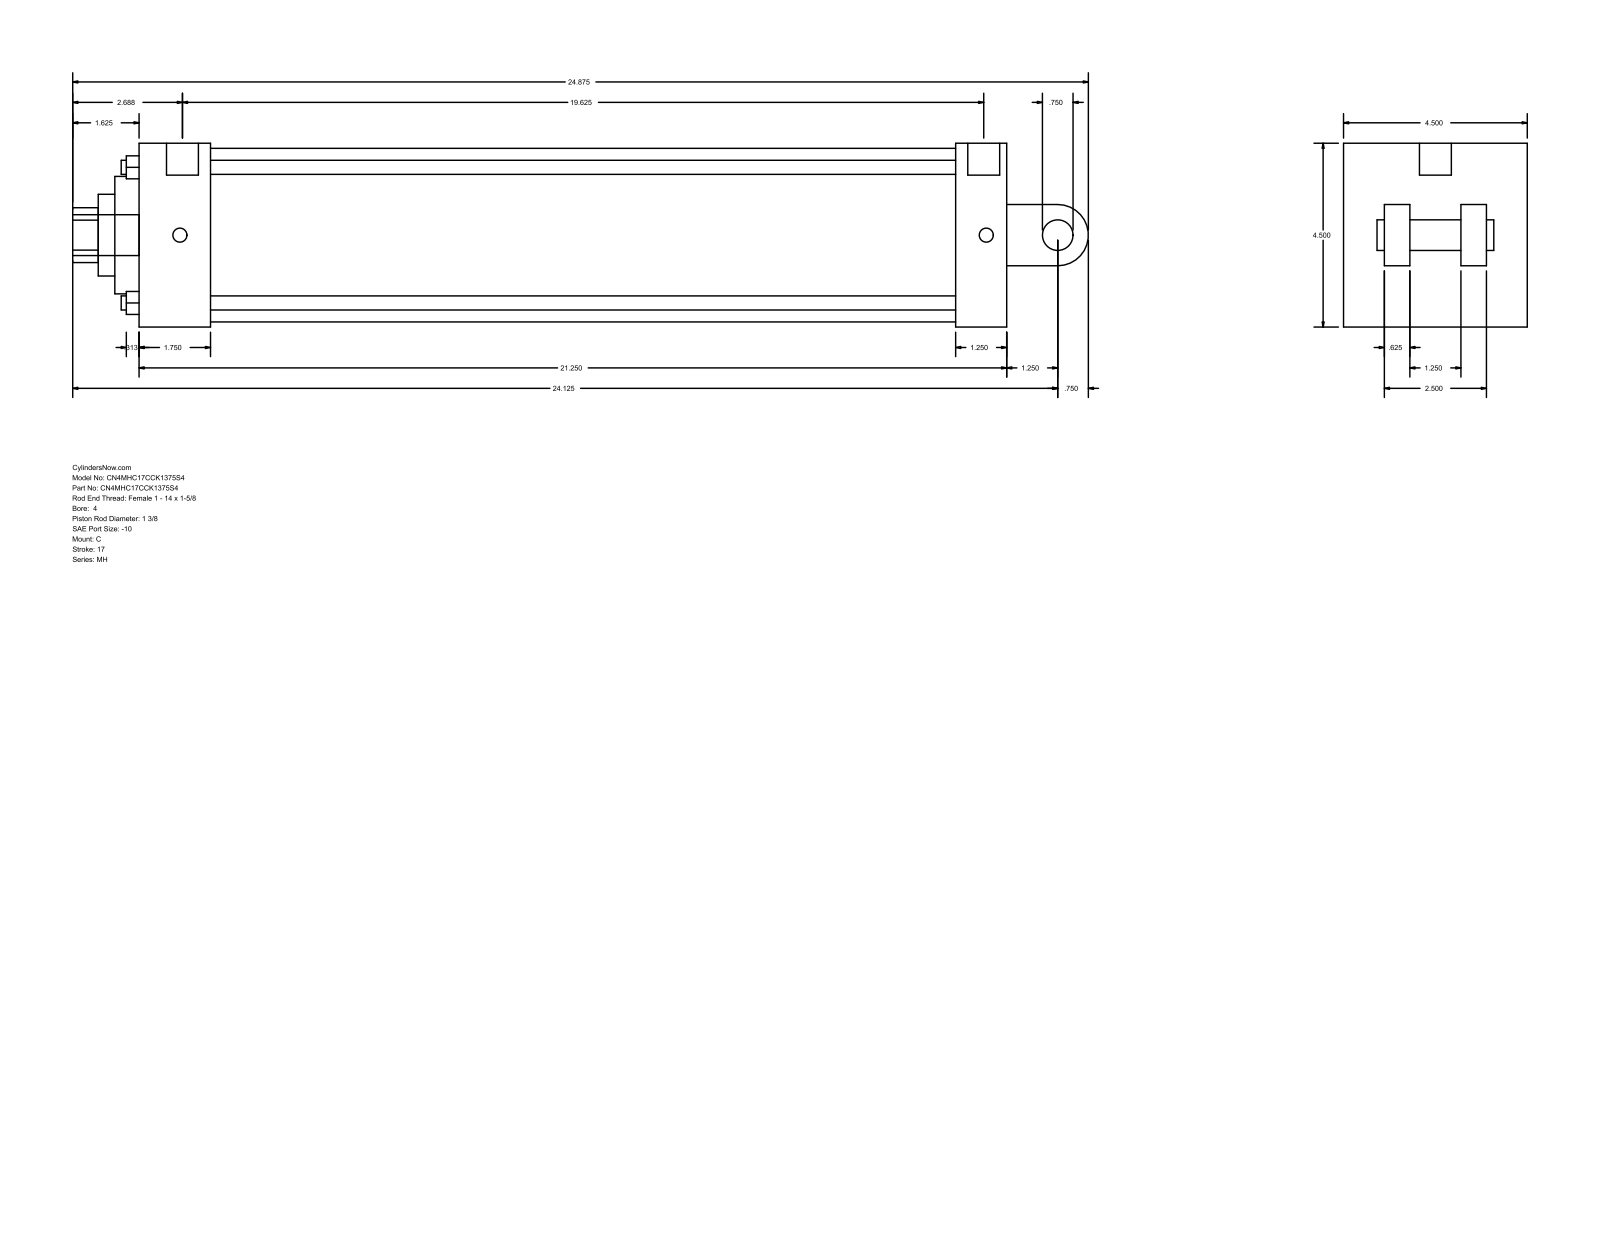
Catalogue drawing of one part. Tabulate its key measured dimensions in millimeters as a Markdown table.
| quantity | value |
| --- | --- |
| part name | MH_C__0400_1.375 |
| STEP written by | GSSL Pune (CONFIG_CONTROL_DESIGN) |
| units | millimeters |
| bodies | 0 solids, 101 faces (71 planar, 30 cylindrical, 0 other) |
| overall size | 631.83 × 114.3 × 114.3 |
| round holes (diameter × count) | 8.76 × 4, 8.73 × 2, 19.84 × 1, 34.92 × 1, 50.8 × 1, 73.03 × 1, 107.95 × 1 |
| round bosses / shafts (diameter × count) | 8.73 × 2, 25.4 × 1, 19.84 × 1, 19.05 × 1 |
| partial cylindrical surfaces (radius × count) | 17.06 × 1, 19.05 × 1 |
| main face-to-face distances | 114.3, 539.75, 44.45, 508, 463.55, 495.3, 31.75, 73.03, 41.27, 38.1 |
| hole center spacings | 59.62, 84.32, 119.25, 1.59 |
